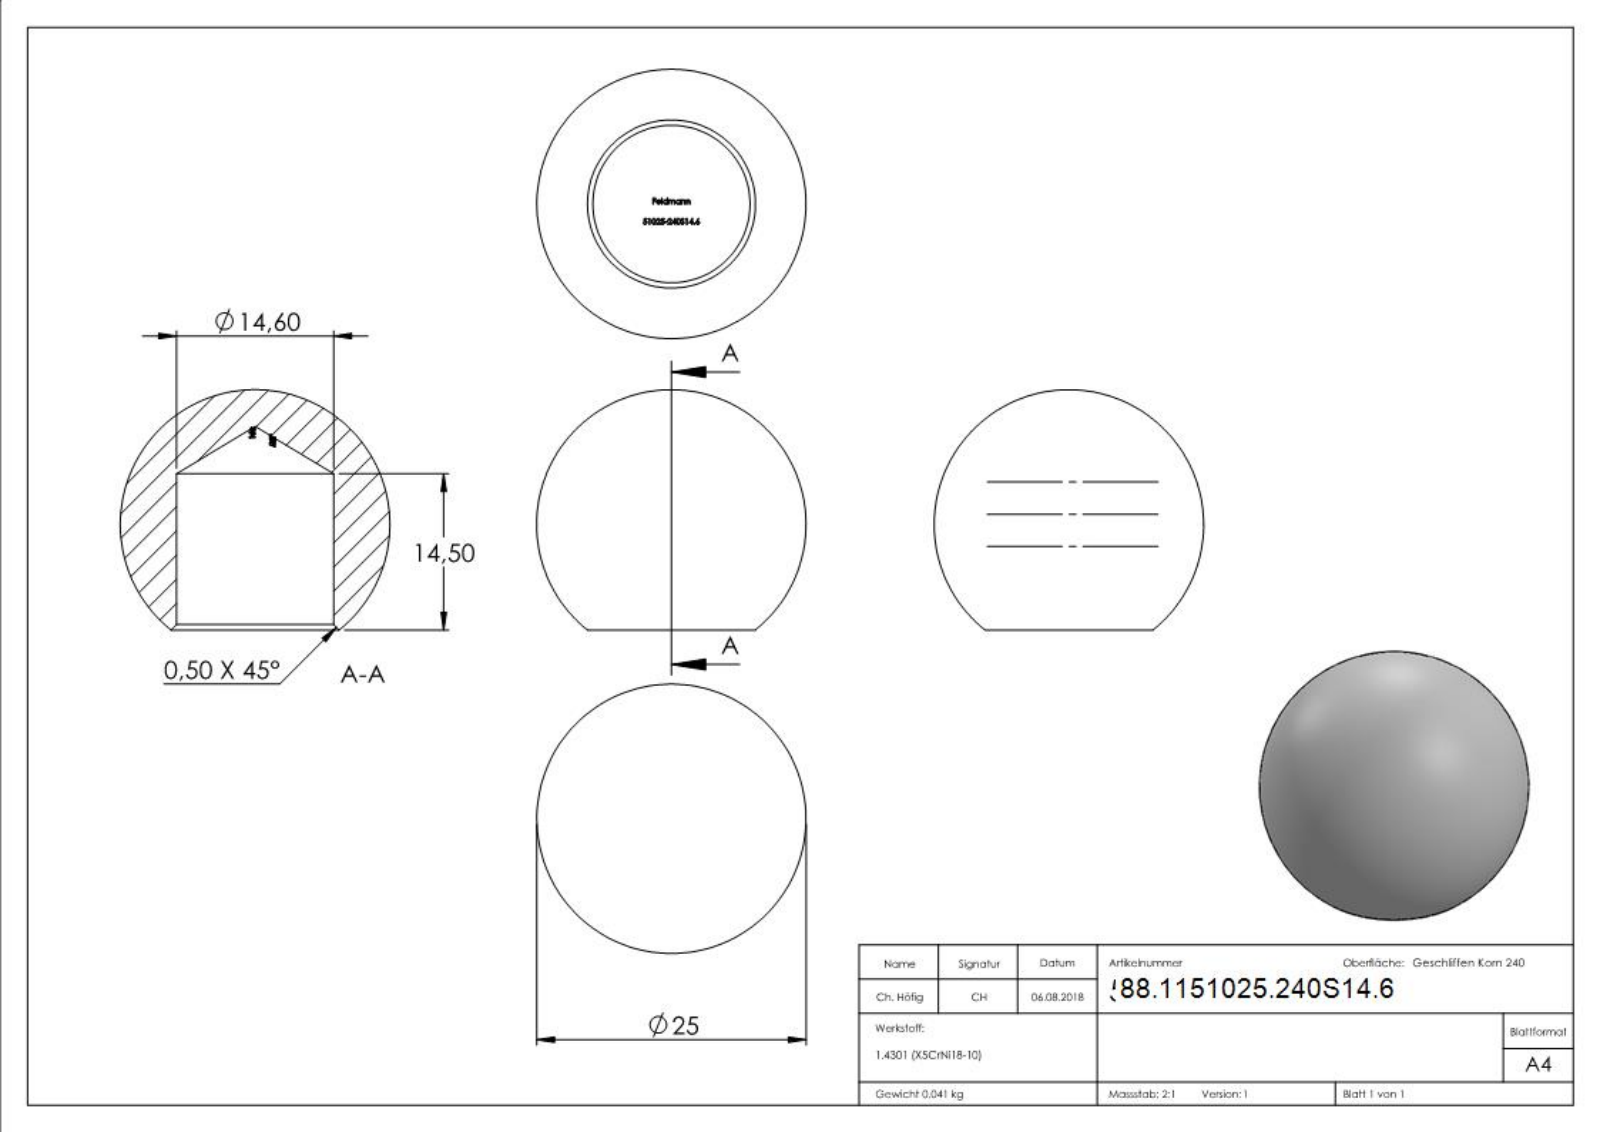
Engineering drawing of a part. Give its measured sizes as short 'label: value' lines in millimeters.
name: 51025-240S14
written by: SolidWorks 2015 (CONFIG_CONTROL_DESIGN)
unit: mm
bodies: 1 solid, 292 faces (125 planar, 2 cylindrical, 165 other)
size: 25 × 25 × 22.27
volume: 5 231 mm³; area: 2 625 mm²
holes: 1× ⌀14.6
face distances: 0.35, 1.31, 2.31, 1.7, 0.5, 0.56, 0.51, 0.55, 1.59, 1.65
